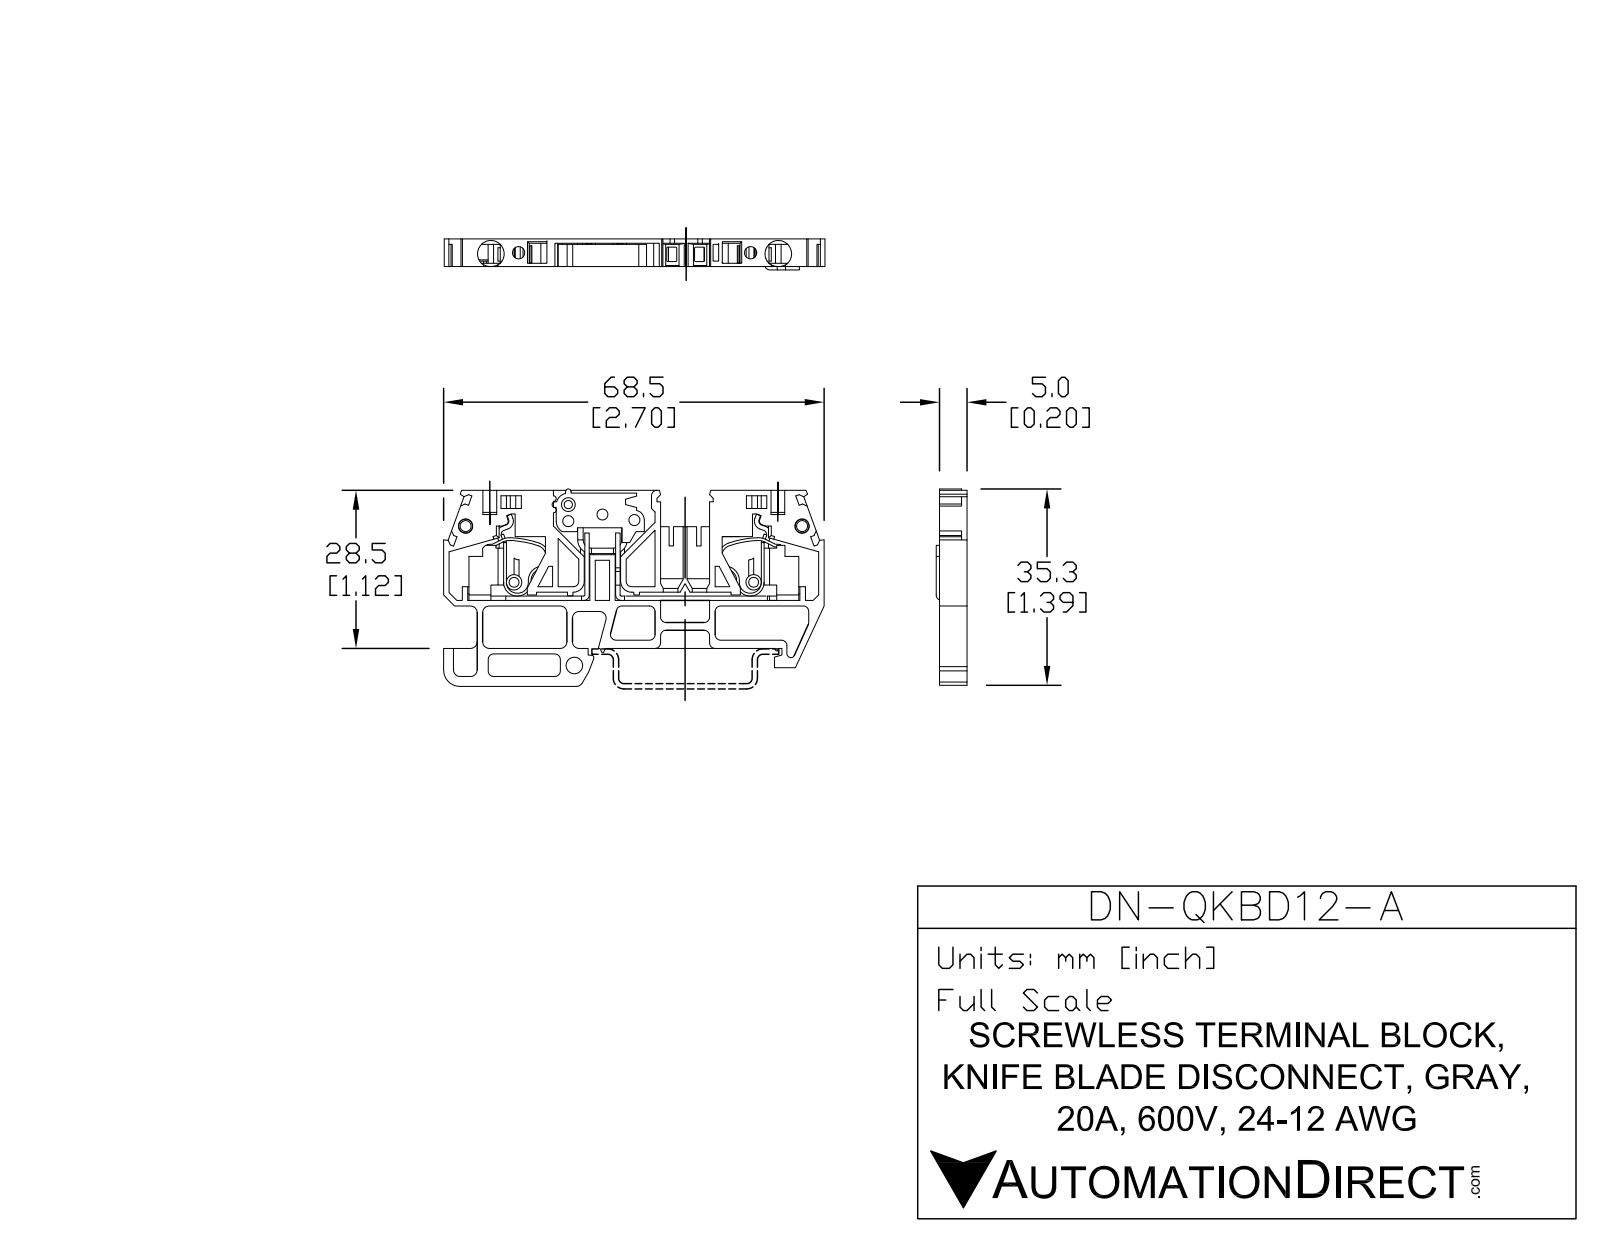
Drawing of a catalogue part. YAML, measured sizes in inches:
part_name: "42419_DN-QKBD12-A"
step_written_by: "SolidWorks 2013 (AUTOMOTIVE_DESIGN)"
units: inches
bodies: {solids: 0, faces: 317, planar: 236, cylindrical: 75, other: 6}
overall_size: [2.701, 1.404, 0.197]
round_holes:
  - {diameter: 0.087, count: 2}
  - {diameter: 0.189, count: 2}
  - {diameter: 0.059, count: 1}
  - {diameter: 0.078, count: 1}
  - {diameter: 0.079, count: 1}
  - {diameter: 0.079, count: 1}
  - {diameter: 0.099, count: 1}
  - {diameter: 0.118, count: 1}
partial_cylinders:
  - {radius: 0.039, count: 20}
  - {radius: 0.047, count: 12}
  - {radius: 0.02, count: 4}
  - {radius: 0.087, count: 2}
  - {radius: 0.098, count: 2}
  - {radius: 0.012, count: 1}
  - {radius: 0.028, count: 1}
  - {radius: 0.071, count: 1}
face_to_face_distances: [0.197, 0.039, 0.028, 0.079, 0.193, 0.118, 0.165, 0.031, 0.047, 0.114]
hole_center_spacings: [0.197, 1.843, 0.118, 0.232, 0.249, 0.254, 0.472, 0.485]
